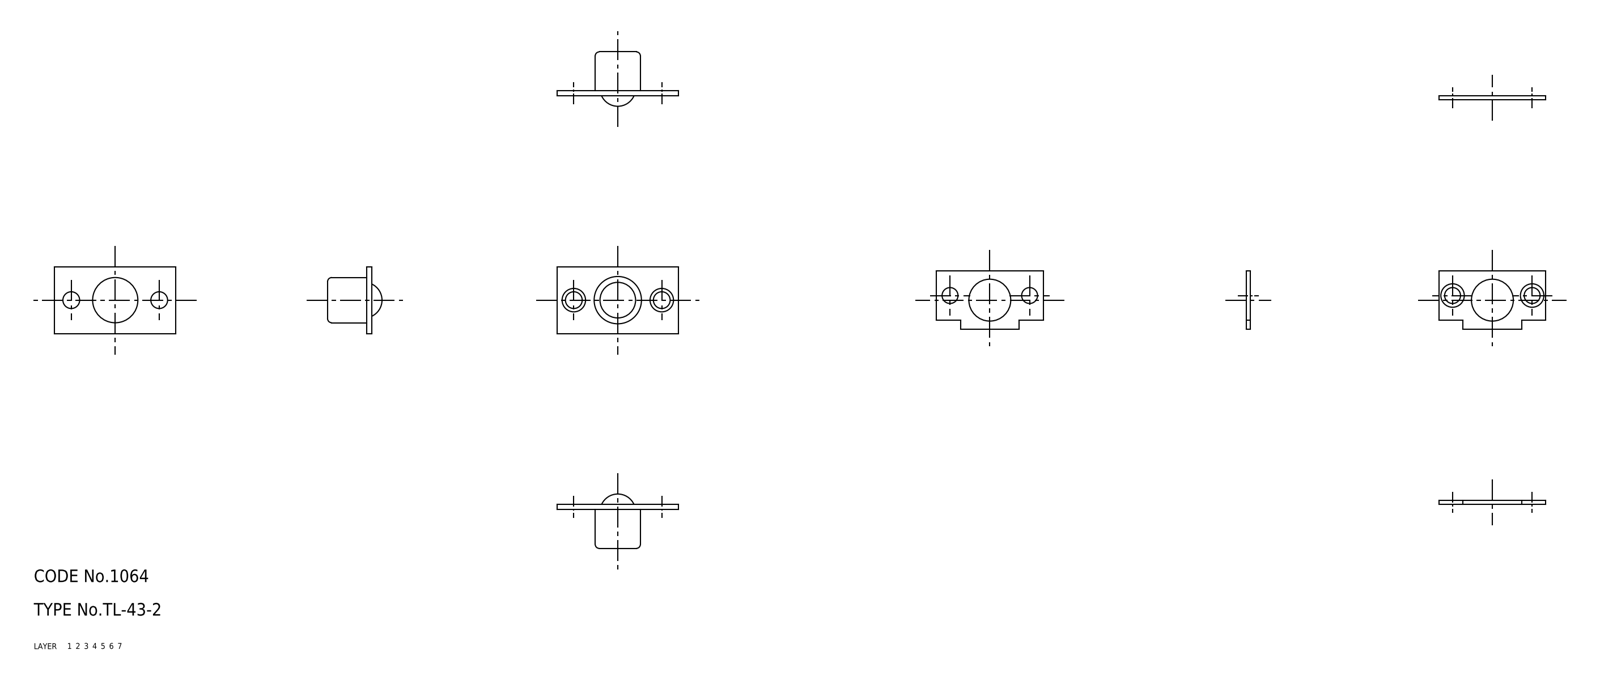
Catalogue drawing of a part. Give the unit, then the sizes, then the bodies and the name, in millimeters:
Units: millimetres
Overall size (bounding box): 36.72 × 29 × 16
Volume: 1 179 mm³ · Surface area: 2 460 mm²
Bodies: 3 solids, 50 faces (0 planar, 0 cylindrical, 50 other)
Part name (STEP PRODUCT): keeper; bracket; ball; TL_43_2_14169_36
STEP written by: CADfix (AUTOMOTIVE_DESIGN)
